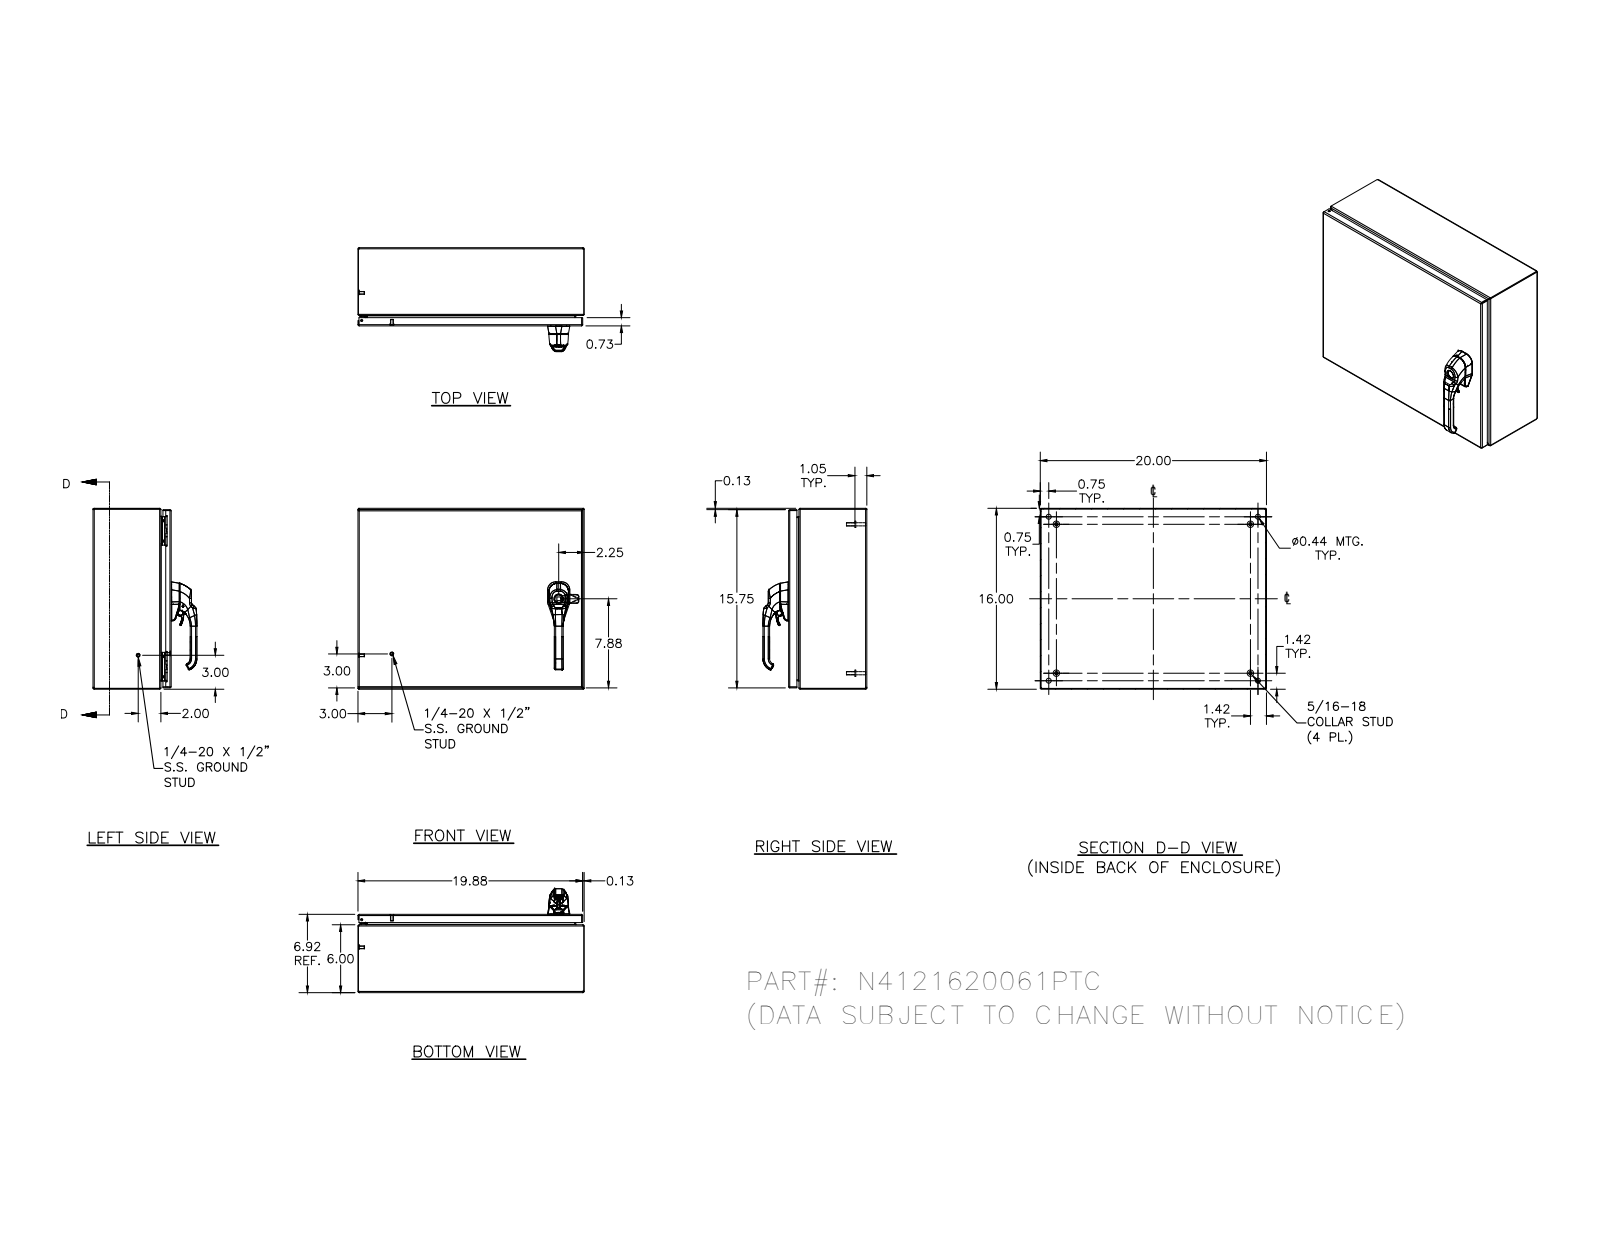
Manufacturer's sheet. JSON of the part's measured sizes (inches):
{"part_name": "N4121620061PTC", "step_written_by": "SolidWorks 2018 (AUTOMOTIVE_DESIGN)", "units": "inches", "bodies": {"solids": 28, "faces": 1280, "planar": 417, "cylindrical": 474, "other": 389}, "overall_size": [20, 16, 9.095], "volume_in3": 99.82, "surface_area_in2": 2491, "round_holes": [[0.188, 5], [0.093, 4], [0.152, 4], [0.167, 4], [0.172, 4], [0.437, 4], [0.28, 3], [0.156, 2], [0.187, 1]], "round_bosses_or_shafts": [[0.25, 10], [0.563, 4], [0.36, 4], [0.32, 4], [0.3, 4], [0.275, 4], [0.256, 4], [0.164, 4]], "partial_cylinders_radius": [[0.031, 30], [0.05, 26], [0.105, 20], [0.016, 18], [0.125, 14], [0.032, 8], [0.067, 8], [0.068, 8]], "face_to_face_distances": [0.074, 6.843, 6.917, 6.769, 15.926, 19.926, 15.852, 16, 20, 19.852], "hole_center_spacings": [11.996, 18.872, 0.017, 0.66, 12.656, 0.019, 0.5, 0.648]}
